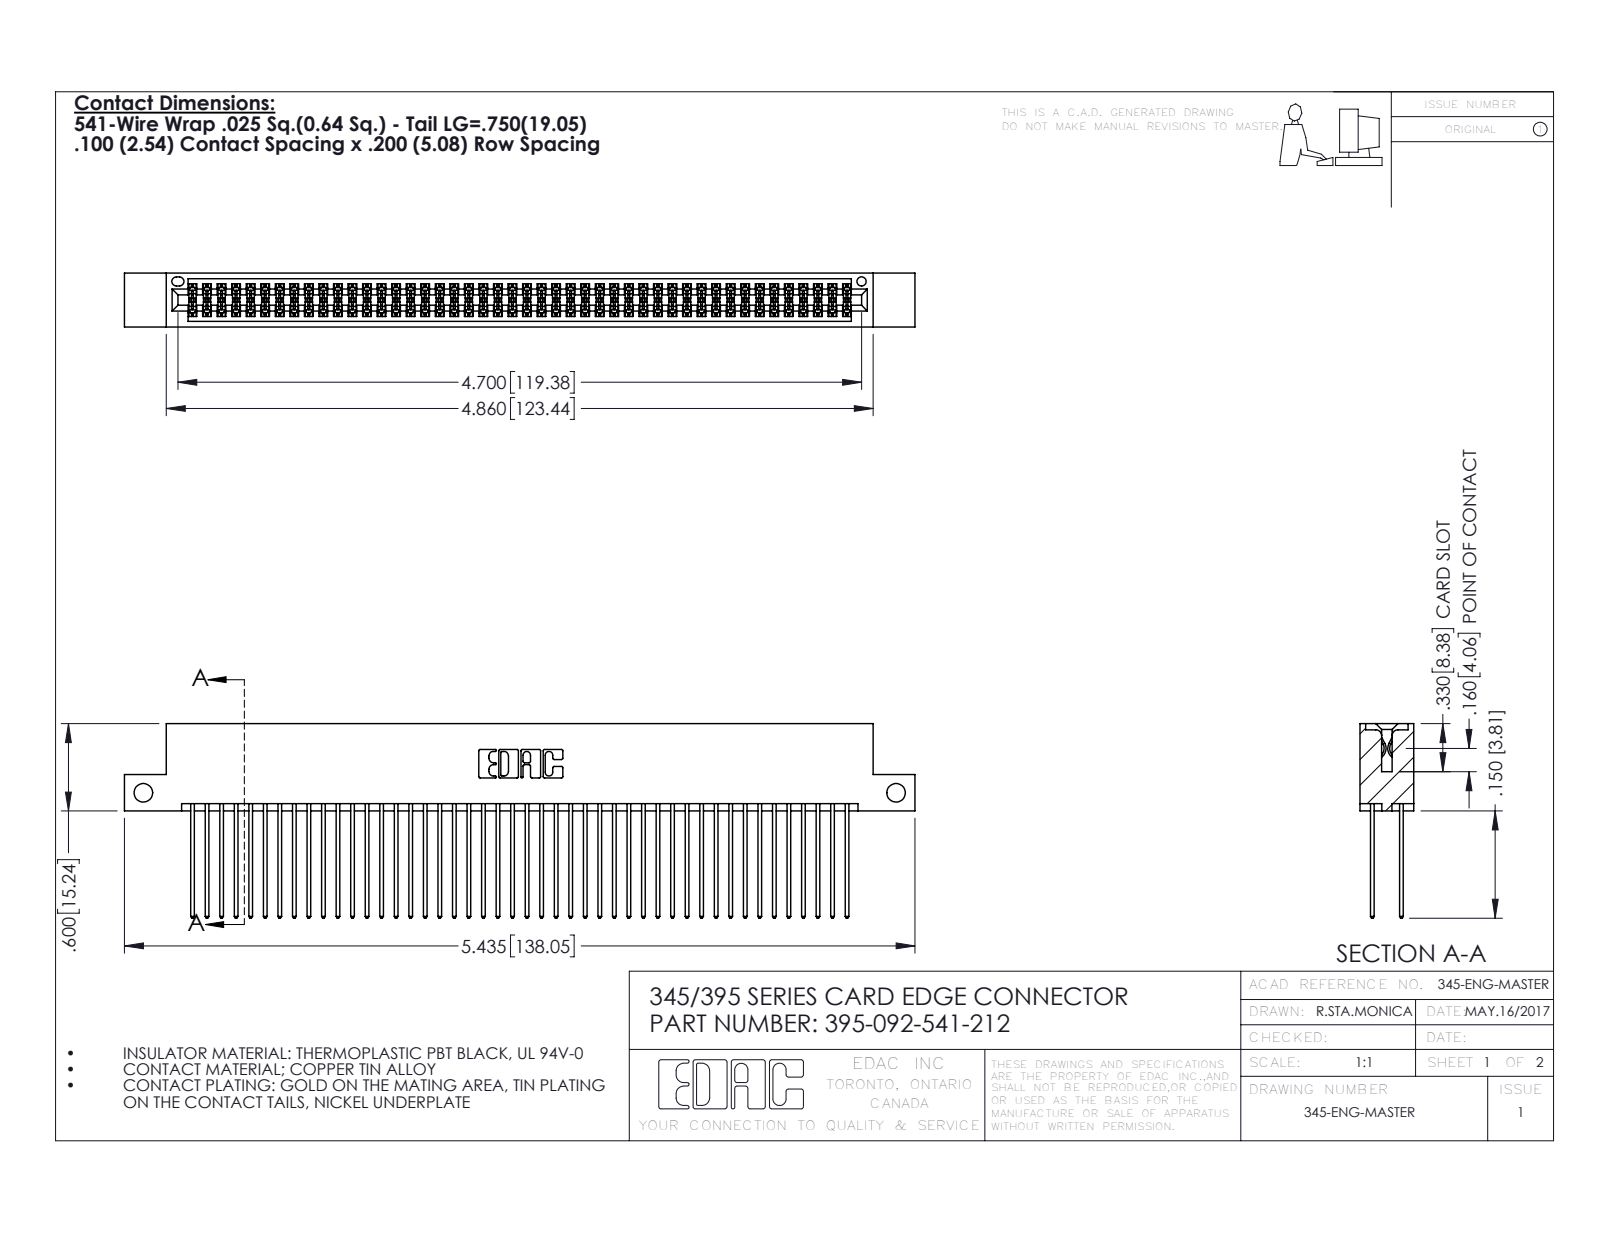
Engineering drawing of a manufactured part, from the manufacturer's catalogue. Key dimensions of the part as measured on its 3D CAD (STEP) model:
Part name (STEP PRODUCT): 345 Part_Flush Mounting Lugs - Side Mount; 395-092-541-212; 345-292-001_345-293-141
STEP written by: SolidWorks 2016 (CONFIG_CONTROL_DESIGN)
Units: inches
Bodies: 93 solids, 4726 faces (3116 planar, 1610 cylindrical, 0 other)
Overall size (bounding box): 5.435 × 1.337 × 0.37
Volume: 0.847 in³ · Surface area: 35.58 in²
Round holes (diameter × count): ⌀0.128 ×2, ⌀0.064 ×1
Partial cylindrical surfaces — rounded edges, fillets, slot ends (radius × count): R0.006 ×138, R0.01 ×92, R0.01 ×22, R0.007 ×6, R0.031 ×6, R0.026 ×3, R0.014 ×2, R0.019 ×2
Main face-to-face distances: 0.298, 0.072, 0.2, 0.098, 0.272, 0.025, 0.225, 0.37, 0.175, 0.149
Hole centre spacings: 5.175
